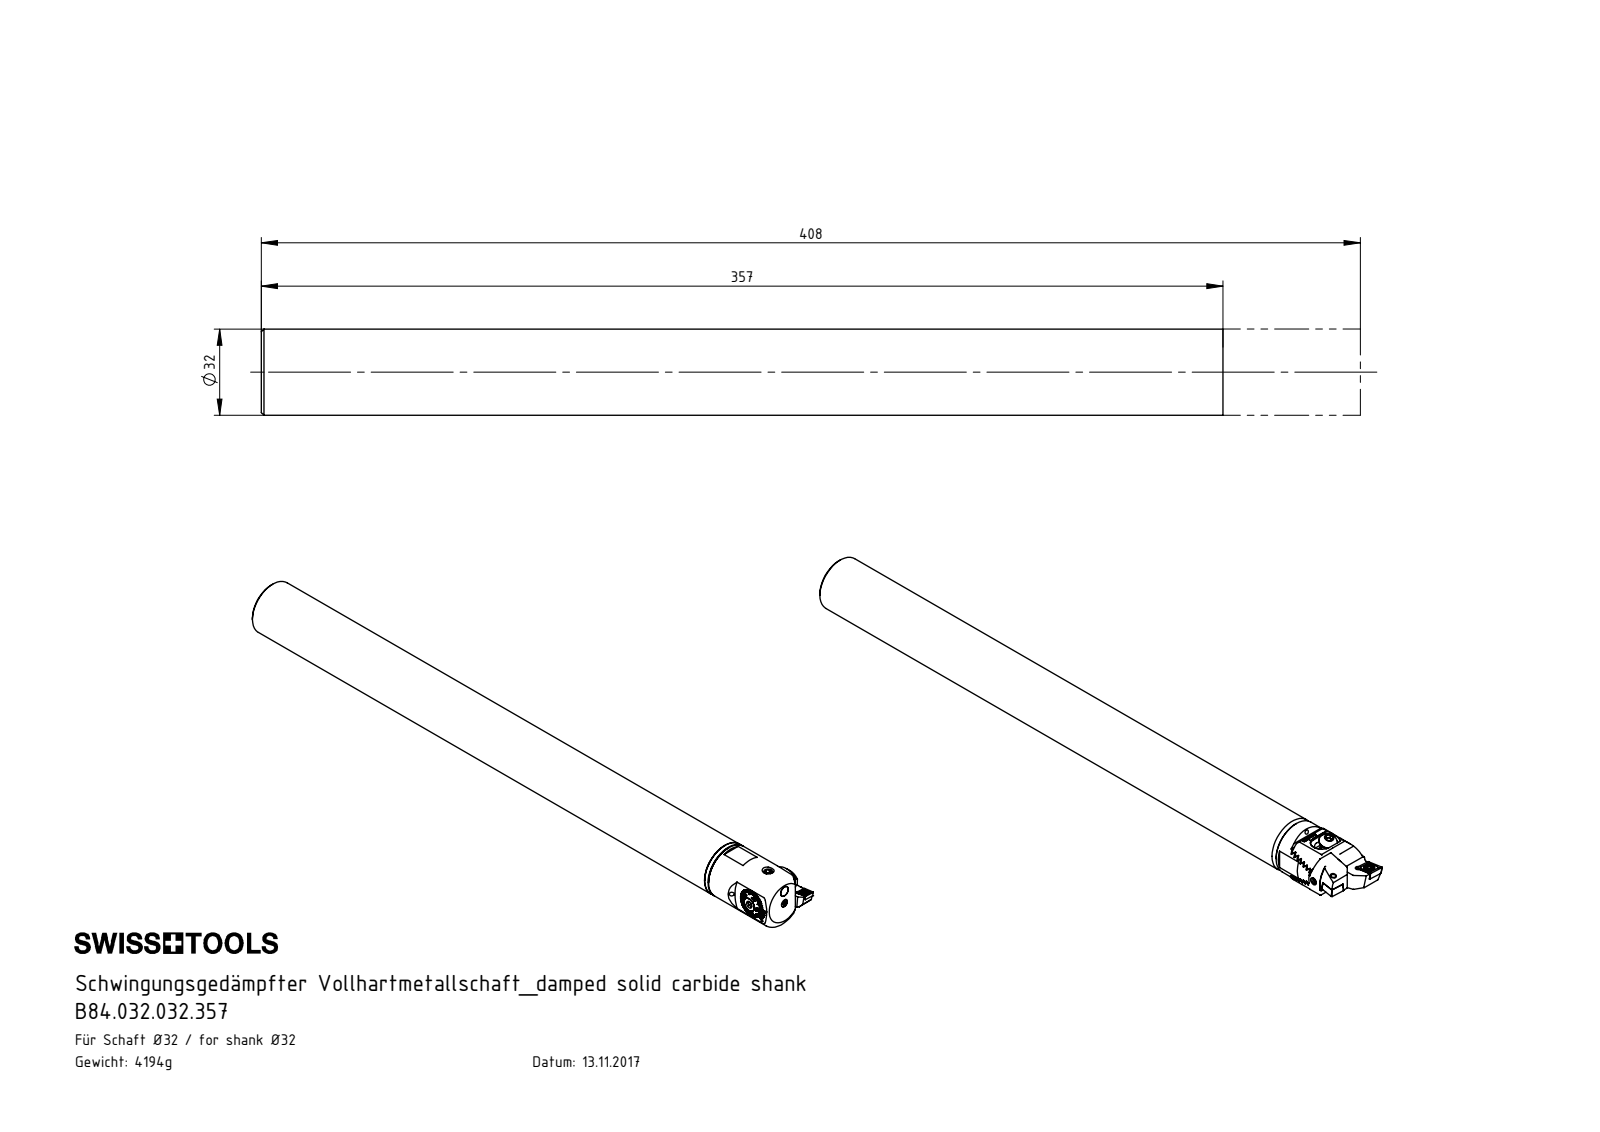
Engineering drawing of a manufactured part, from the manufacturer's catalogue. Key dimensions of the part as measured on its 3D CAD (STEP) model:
Part name (STEP PRODUCT): B84.032.032.357; HP5-ER1.019.036_A; HP5-Z32.040.051_fr Zeichnung; Z32-WCB.001.021 (+8 more)
STEP written by: SolidWorks 2017 (CONFIG_CONTROL_DESIGN)
Units: millimetres
Bodies: 16 solids, 976 faces (446 planar, 238 cylindrical, 292 other)
Overall size (bounding box): 408 × 40 × 32
Volume: 303 486 mm³ · Surface area: 63 883 mm²
Round holes (diameter × count): ⌀2.5 ×5, ⌀3.3 ×4, ⌀1.6 ×2, ⌀2 ×2, ⌀4.4 ×2, ⌀5 ×2, ⌀6.1 ×2, ⌀6.4 ×2, ⌀6.8 ×2, ⌀3.5 ×1, ⌀4.2 ×1, ⌀10.2 ×1
Round bosses / shafts (diameter × count): ⌀4 ×4, ⌀10.5 ×2, ⌀10.2 ×2, ⌀6 ×2, ⌀5.25 ×2, ⌀32 ×1, ⌀3 ×1, ⌀2.2 ×1
Partial cylindrical surfaces — rounded edges, fillets, slot ends (radius × count): R0.5 ×16, R0.2 ×14, R0.2 ×12, R0.34 ×12, R0.59 ×12, R2 ×4, R3.3 ×4, R6 ×4
Main face-to-face distances: 2.38, 4.76, 7.14, 3, 357, 360, 9.52, 36, 39, 321
Hole centre spacings: 6.07, 6.19, 24.22, 24.33, 28.65, 9, 9.01, 17.39
